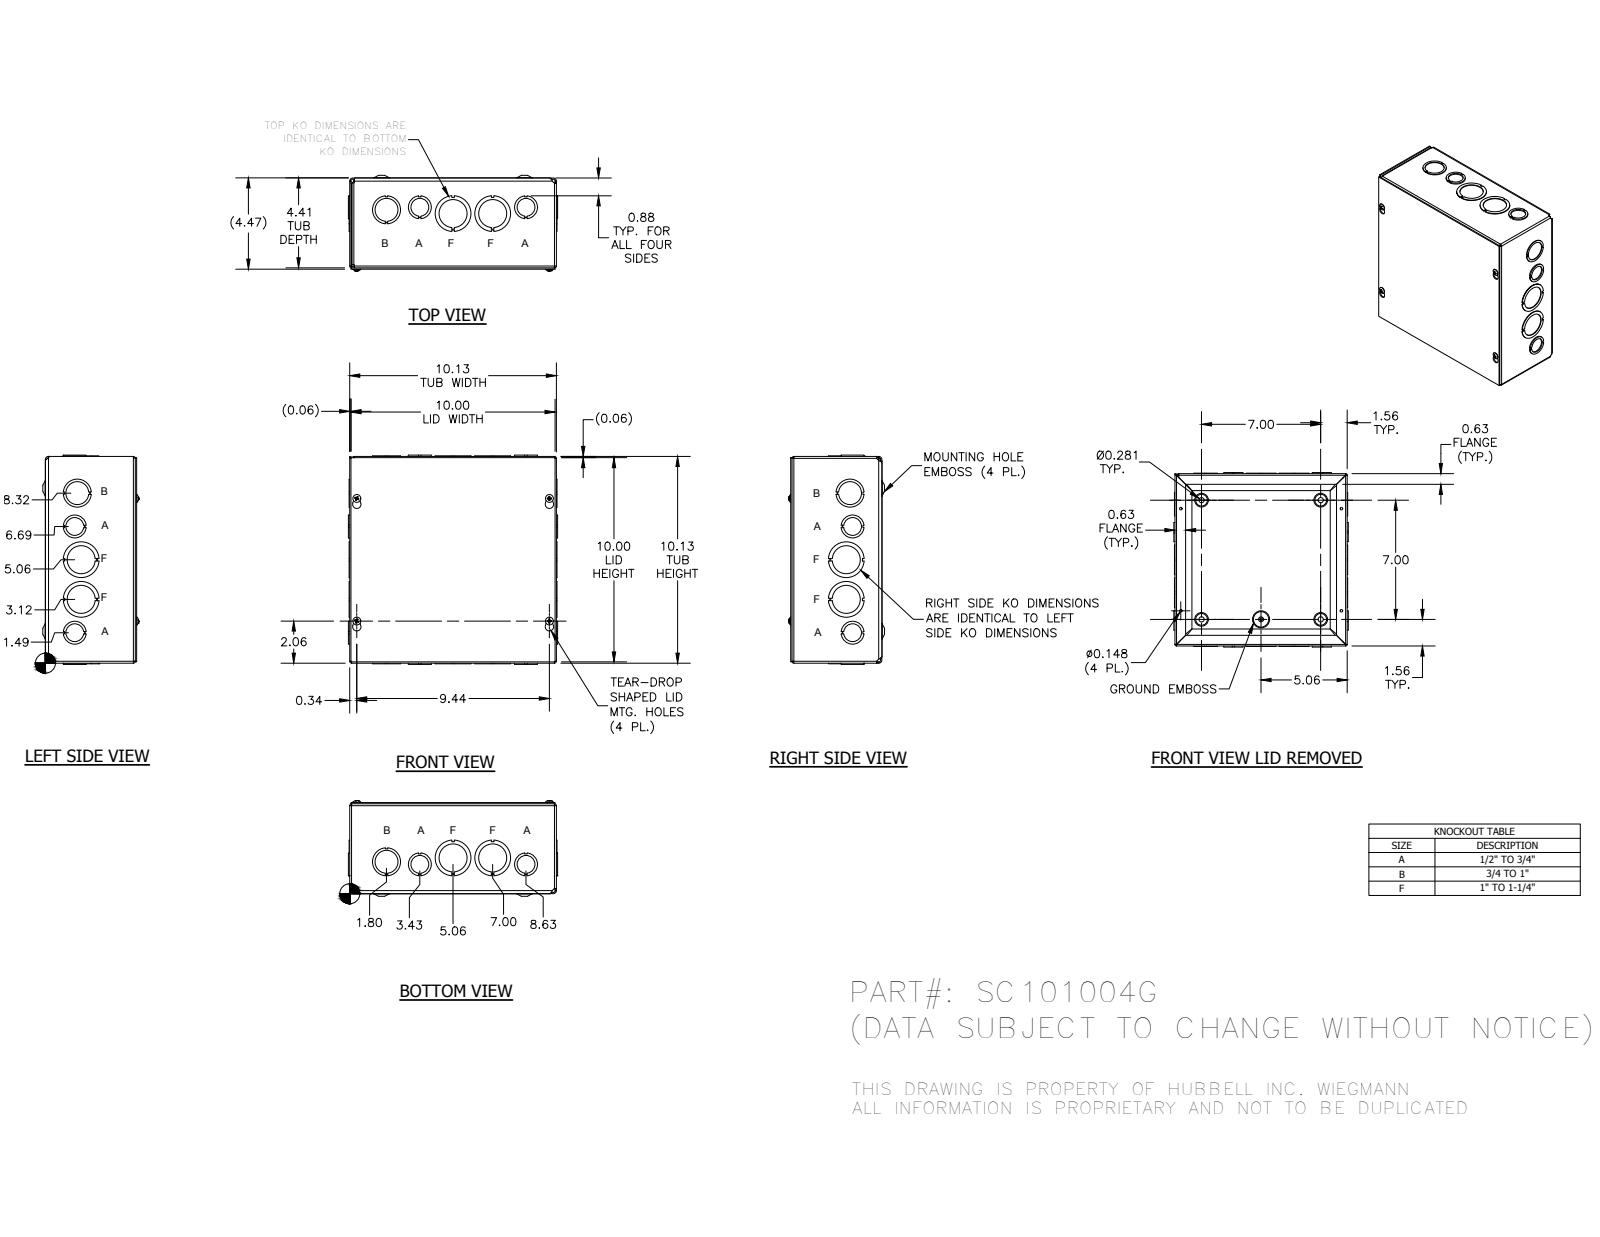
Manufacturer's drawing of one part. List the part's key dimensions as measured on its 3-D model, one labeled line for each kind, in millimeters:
Part name (STEP PRODUCT): SC1010GBKP; SC101004GWRA; SC1010GLID; 34056 (+1 more)
STEP written by: Autodesk Inventor 2014 (AUTOMOTIVE_DESIGN)
Units: millimetres
Bodies: 22 solids, 918 faces (574 planar, 193 cylindrical, 151 other)
Overall size (bounding box): 260.32 × 260.32 × 119.2
Round holes (diameter × count): ⌀28.57 ×6, ⌀34.92 ×6, ⌀3.76 ×4, ⌀7.62 ×4, ⌀22.22 ×4, ⌀44.45 ×4, ⌀4.19 ×1
Round bosses / shafts (diameter × count): ⌀9.75 ×4, ⌀4.17 ×4, ⌀5.8 ×1
Partial cylindrical surfaces — rounded edges, fillets, slot ends (radius × count): R0.79 ×8, R2.37 ×8, R1.4 ×4, R1.57 ×4, R2.38 ×4, R2.79 ×4, R2.97 ×4, R3.15 ×4
Main face-to-face distances: 1.57, 255.6, 110.32, 111.89, 1.59, 111.91, 113.48, 257.17, 254.03, 1.58
Hole centre spacings: 167.98, 177.8, 42.15, 91.03, 33.45, 33.46, 88.9, 132.08
